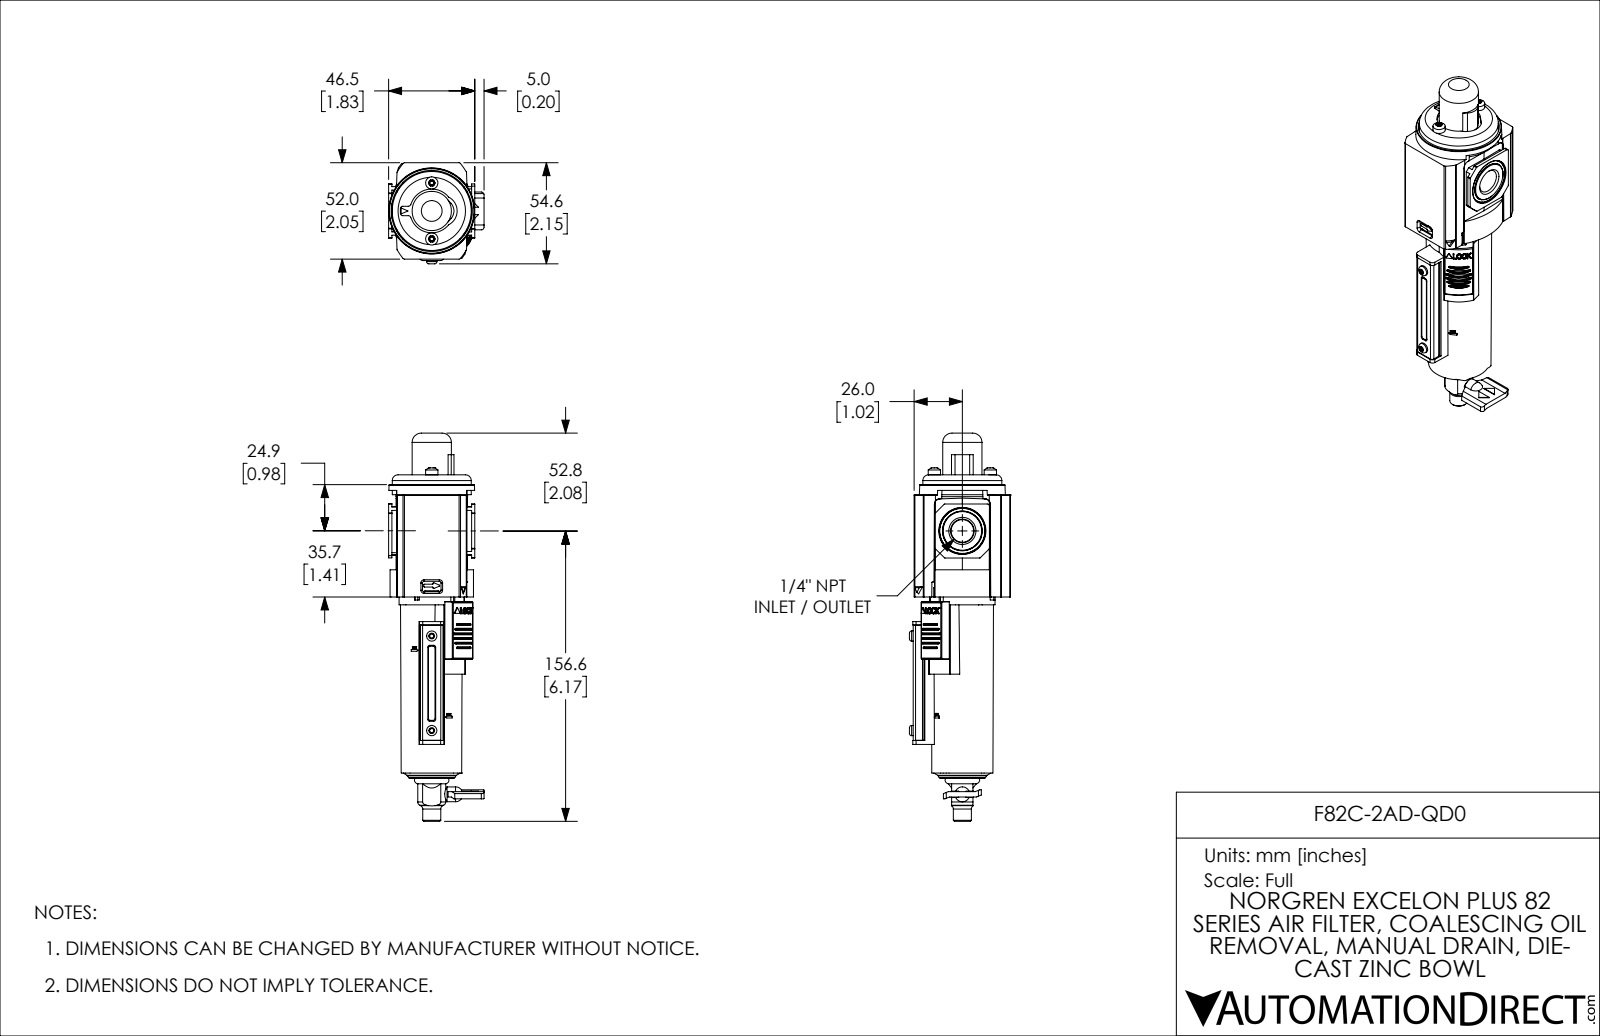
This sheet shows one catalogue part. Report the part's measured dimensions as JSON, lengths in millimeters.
{"part_name": "F82C-2AD-QD0", "step_written_by": "SolidWorks 2021 (CONFIG_CONTROL_DESIGN)", "units": "millimeters", "bodies": {"solids": 8, "faces": 1211, "planar": 526, "cylindrical": 481, "other": 204}, "overall_size": [209.4, 54.6, 51.5], "volume_mm3": 232000, "surface_area_mm2": 62360, "round_holes": [[1.5, 2], [2, 2], [3.3, 2], [4.4, 2], [6.4, 1], [16, 1]], "round_bosses_or_shafts": [[6.6, 2], [5.5, 2], [4, 2], [42.6, 1], [38.7, 1], [35.3, 1], [34.4, 1], [32.8, 1]], "partial_cylinders_radius": [[0.5, 73], [1, 38], [0.3, 12], [0.5, 12], [0.3, 10], [0.8, 8], [0.9, 8], [1.2, 8]], "face_to_face_distances": [1.5, 50.5, 52, 49, 48.2, 4.6, 34.3, 37.5, 3.1, 6], "hole_center_spacings": [20.2, 13.5, 15.1, 15.1, 30.2, 27, 30.2, 30.2]}
